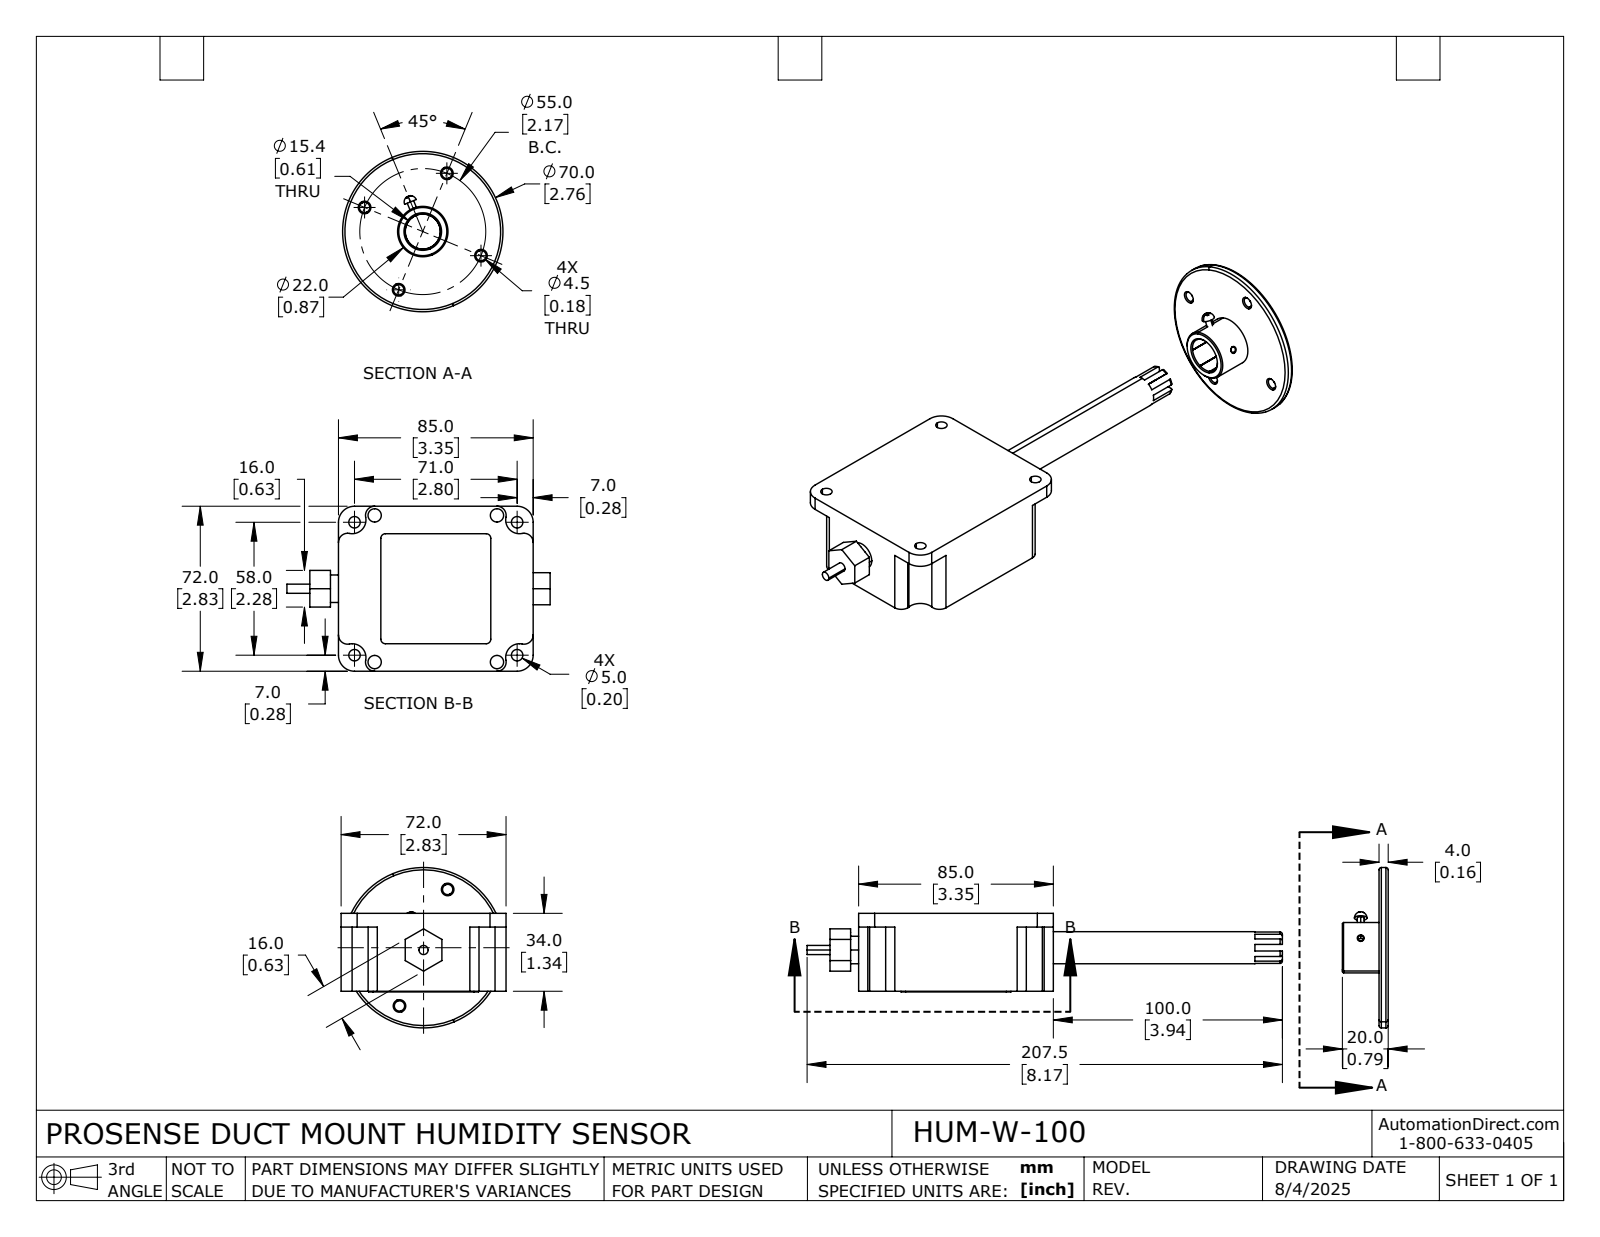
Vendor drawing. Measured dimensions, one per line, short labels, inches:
name: HUM-W-100
written by: SolidWorks 2024 (AUTOMOTIVE_DESIGN)
unit: in
bodies: 4 solids, 203 faces (70 planar, 83 cylindrical, 50 other)
size: 9.988 × 2.835 × 2.756
volume: 13.78 in³; area: 60.21 in²
holes: 4× ⌀0.177, 4× ⌀0.197, 4× ⌀0.228, 2× ⌀0.098
bosses: 1× ⌀2.756, 1× ⌀0.866, 1× ⌀0.551, 1× ⌀0.472, 1× ⌀0.157, 1× ⌀0.118
rounds: 8× R0.157, 6× R0.004, 4× R0.079, 4× R0.236, 4× R0.276, 1× R0.033
face distances: 0.157, 1.339, 1.35, 2.835, 9.102, 8.944, 5.756, 5.598, 3.346, 1.102
hole spacings: 0.366, 2.426, 2.452, 3.43, 1.531, 2.102, 2.165, 2.283
